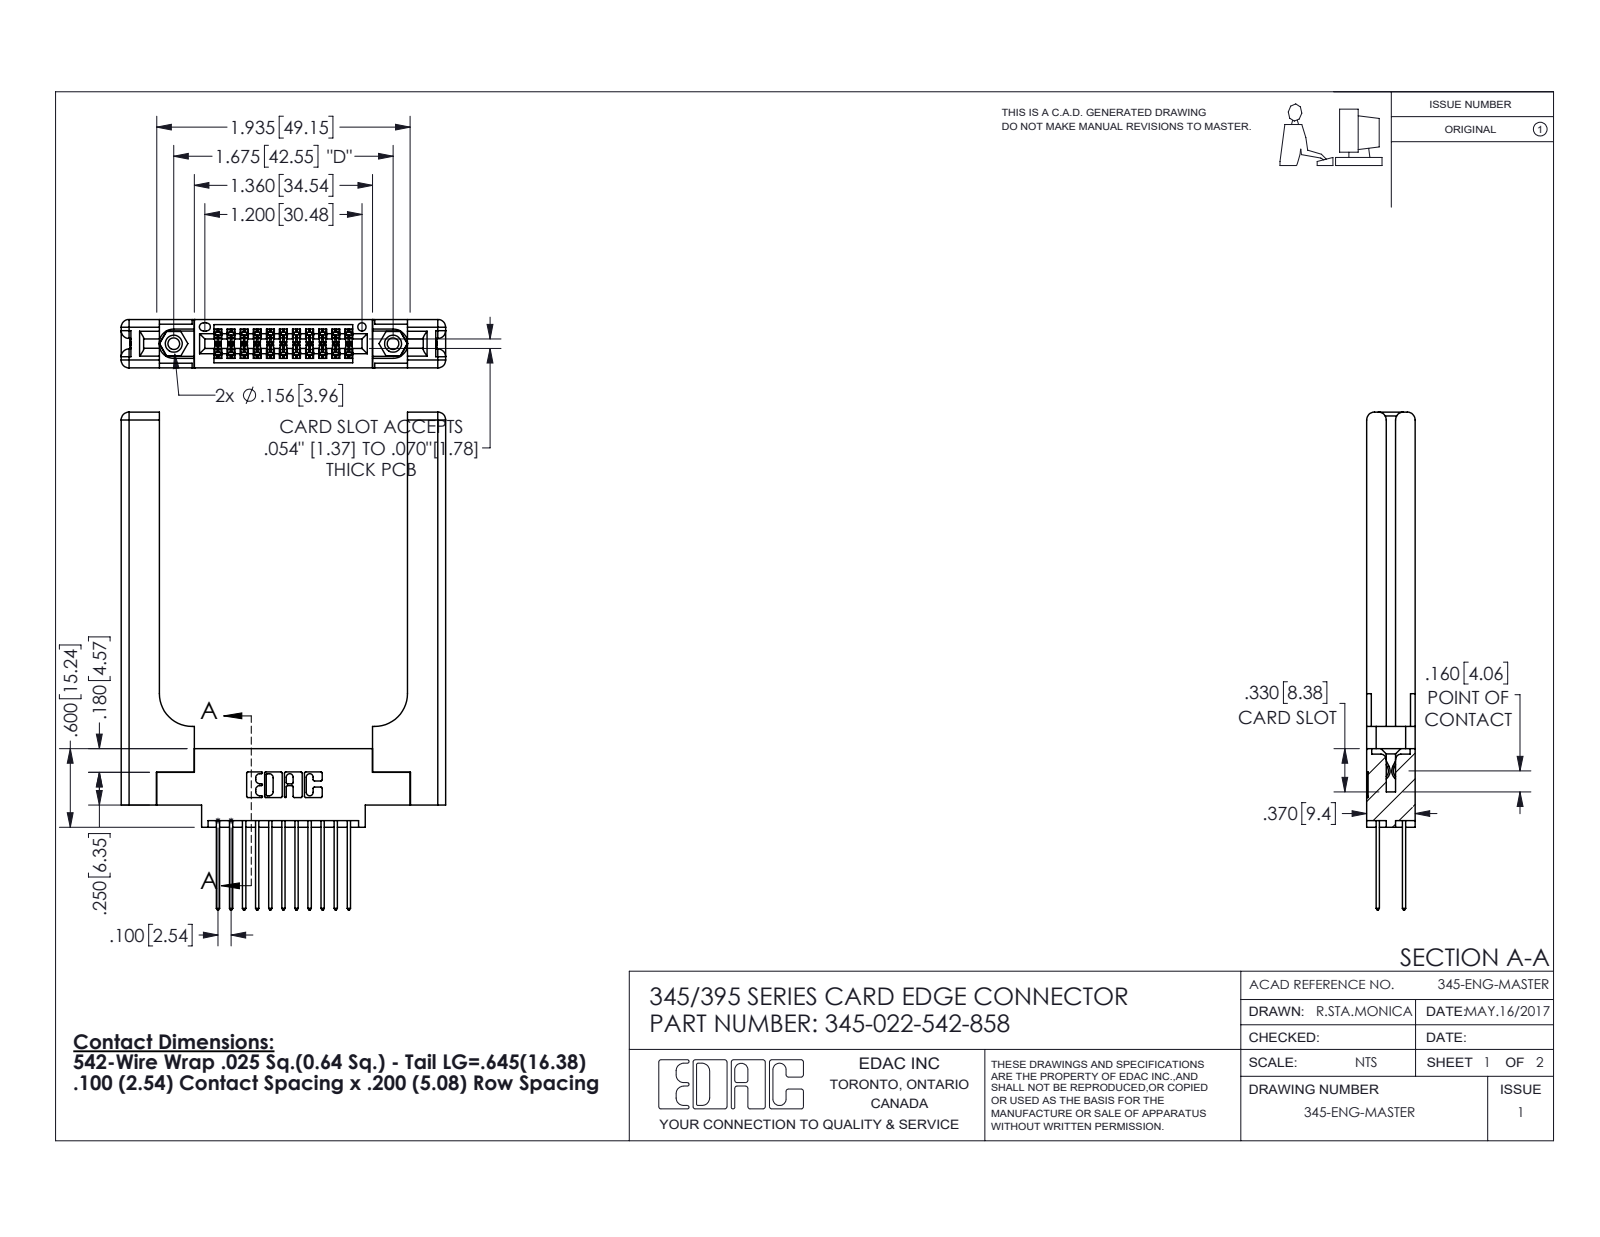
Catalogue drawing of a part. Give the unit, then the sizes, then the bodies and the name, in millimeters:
Units: millimetres
Overall size (bounding box): 96.6 × 63 × 9.4
Round holes (diameter × count): ⌀2.3 ×2, ⌀3.2 ×2, ⌀4 ×2, ⌀1.6 ×1
Round bosses / shafts (diameter × count): ⌀3.9 ×2
Partial cylindrical surfaces — rounded edges, fillets, slot ends (radius × count): R0.2 ×33, R0.3 ×22, R0.3 ×22, R1.5 ×16, R0.2 ×6, R0.8 ×6, R0.7 ×3, R0.4 ×2
Main face-to-face distances: 9.4, 1.8, 7.6, 3.8, 3.8, 2, 5.6, 3.1, 2.5, 6.9
Hole centre spacings: 6.9, 36.7, 42.5
Volume: 14 300 mm³ · Surface area: 13 680 mm²
Bodies: 27 solids, 1486 faces (958 planar, 468 cylindrical, 60 other)
Part name (STEP PRODUCT): 345-250-001_345-250-001-102; 345 Part_0.170 Offset - 0.156 Dia-TH; 345-022-542-858; 345-220-058_345-220-058 (+1 more)
STEP written by: SolidWorks 2016 (CONFIG_CONTROL_DESIGN)
